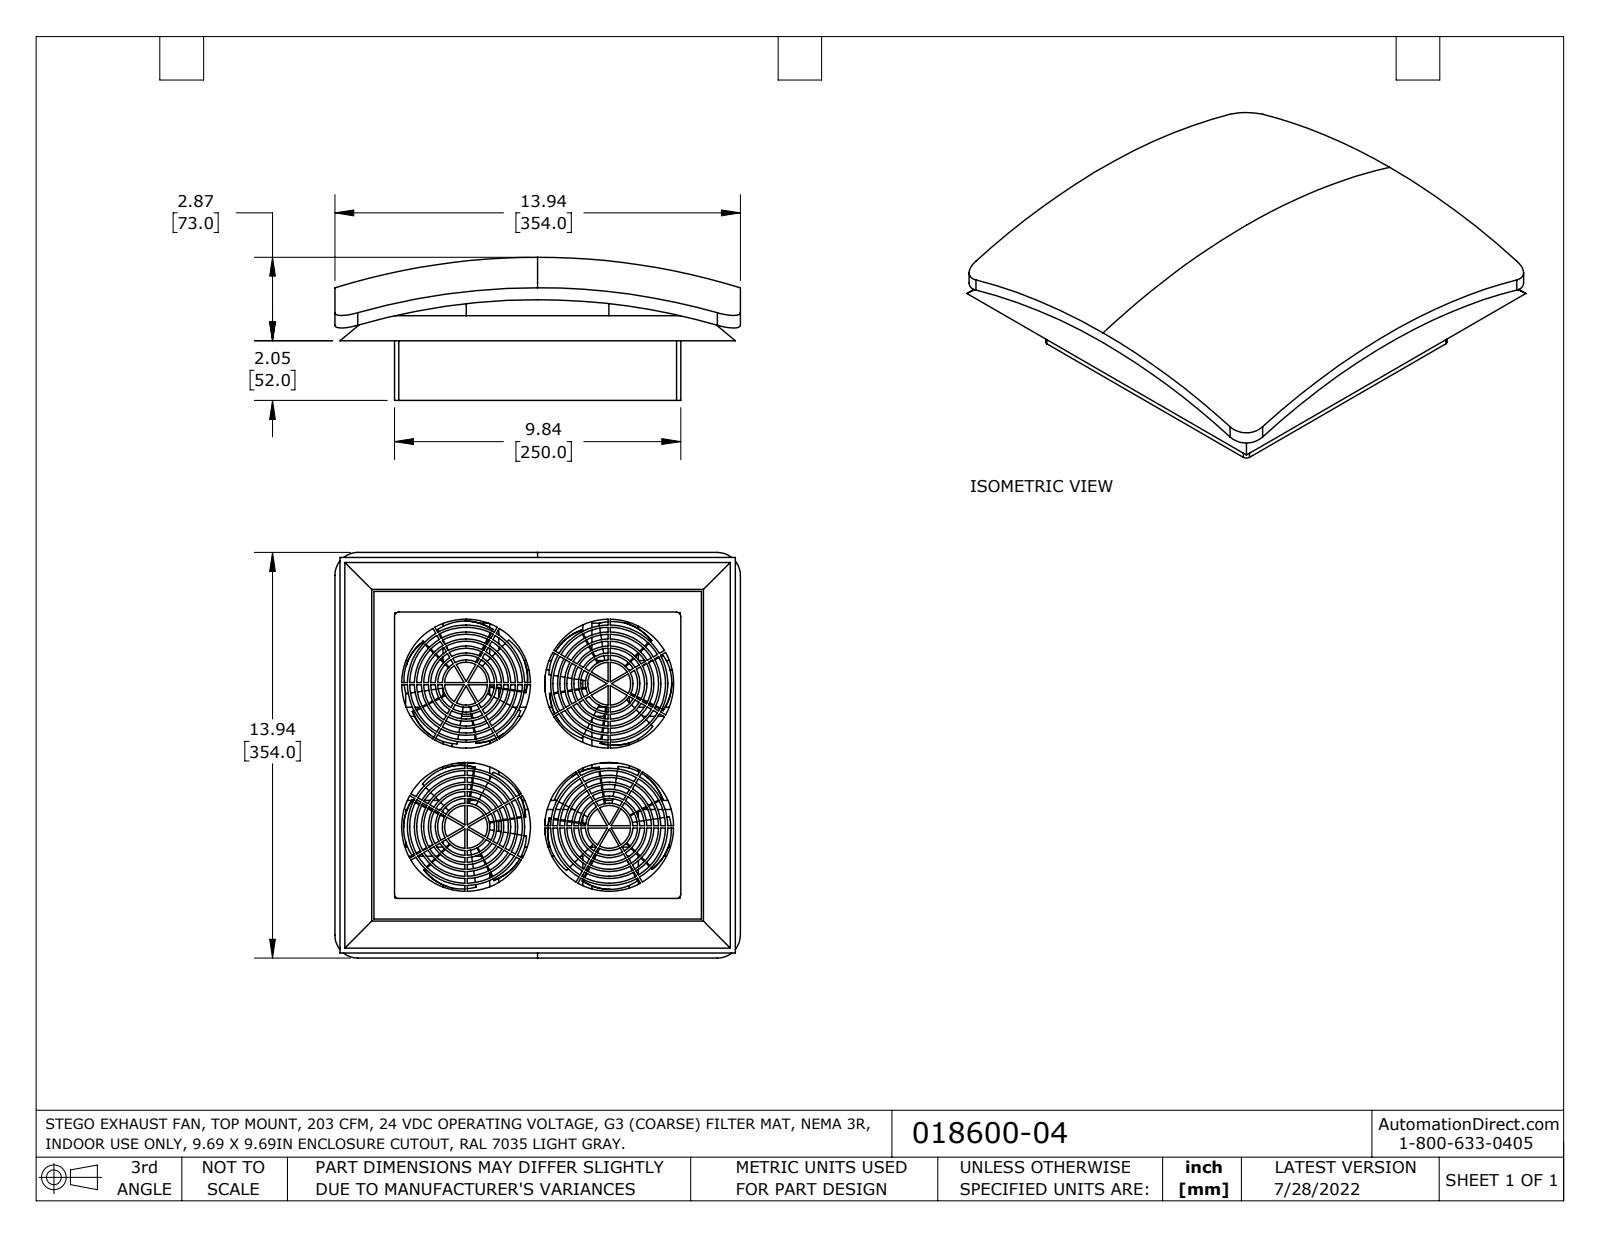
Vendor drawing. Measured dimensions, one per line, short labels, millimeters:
name: 018600-04_Default
written by: SolidWorks 2021 (CONFIG_CONTROL_DESIGN)
unit: mm
bodies: 1 solid, 1107 faces (675 planar, 428 cylindrical, 4 other)
size: 354 × 354 × 125
volume: 4 225 000 mm³; area: 907 700 mm²
holes: 4× ⌀37.4, 4× ⌀49.6, 4× ⌀61.7, 4× ⌀73.9, 4× ⌀86.1, 4× ⌀98.3, 4× ⌀112.5
bosses: 4× ⌀102.3, 4× ⌀77.9, 4× ⌀65.8, 4× ⌀53.6, 4× ⌀41.4, 4× ⌀39.4, 2× ⌀90.1, 2× ⌀90.1
rounds: 12× R54.6, 8× R54.6, 4× R3.8, 4× R20
face distances: 10.9, 21.9, 52, 2.8, 62.9, 73.9, 2, 250, 56.4, 4.4
hole spacings: 125, 176.8
